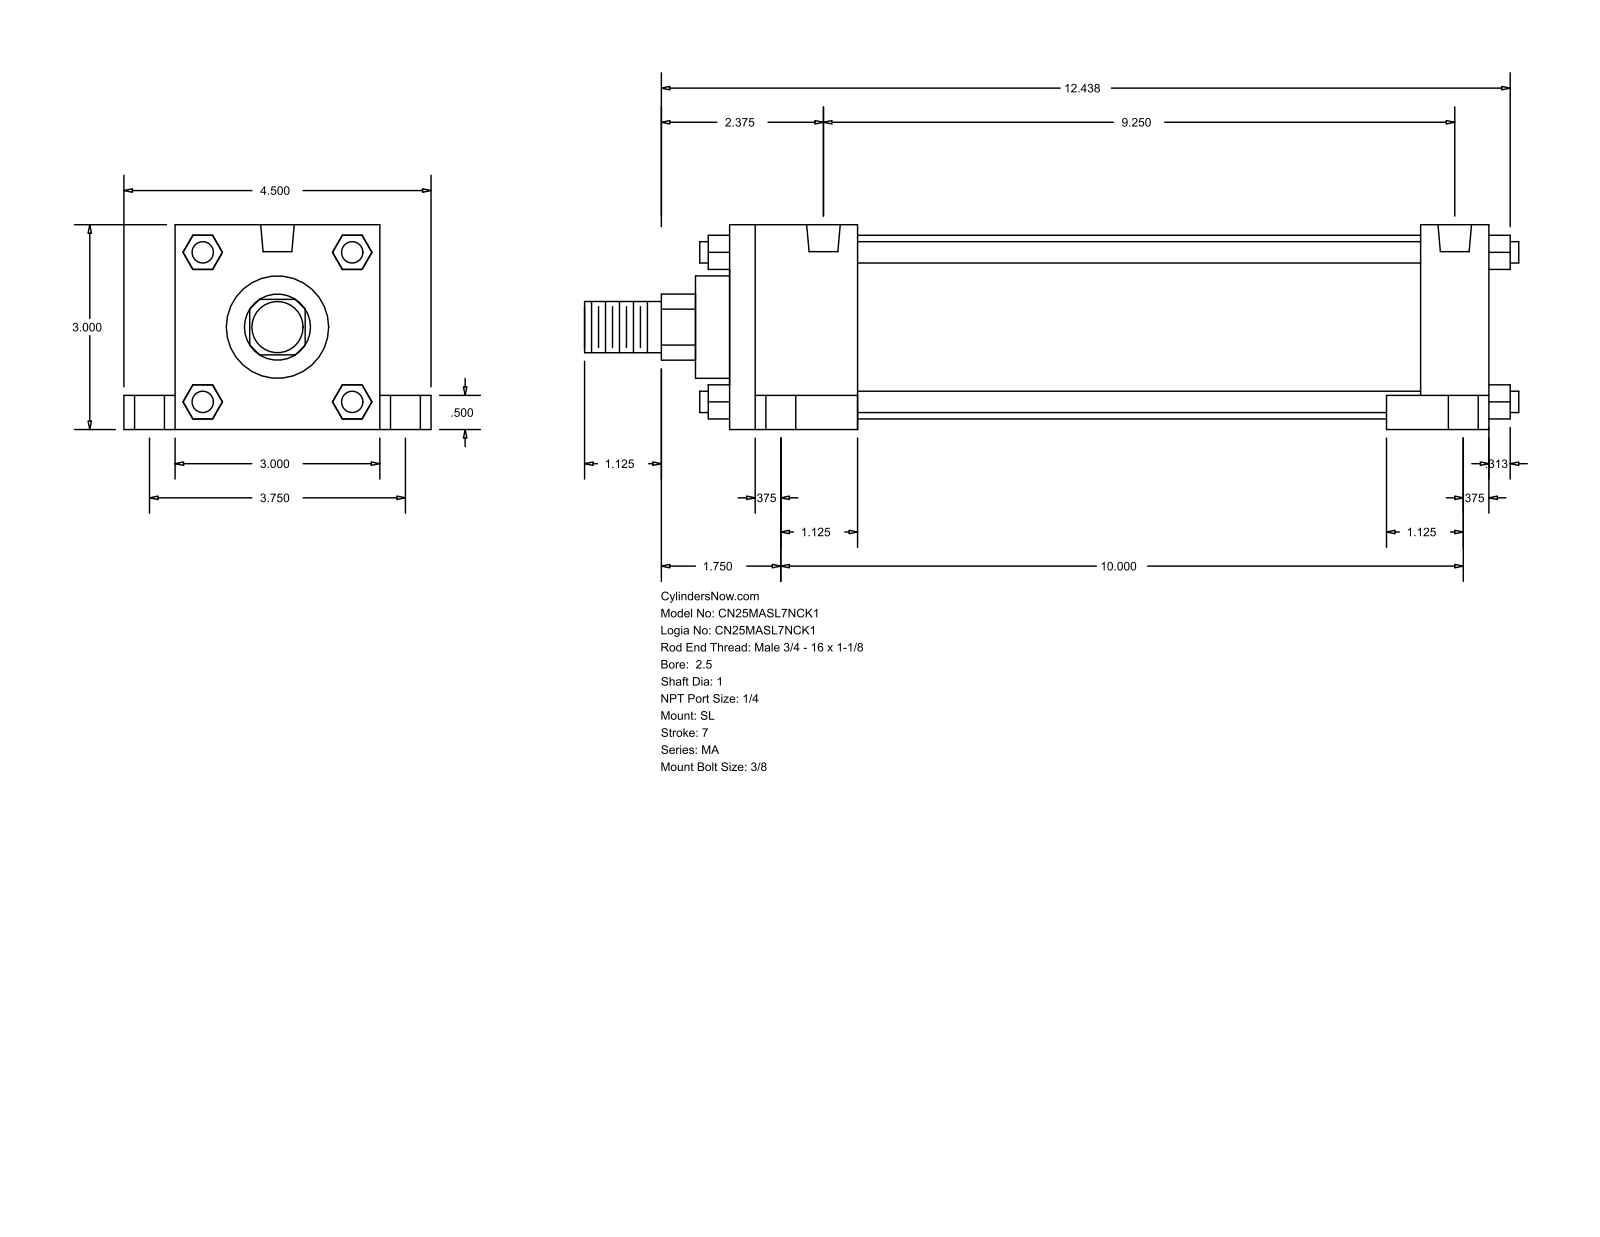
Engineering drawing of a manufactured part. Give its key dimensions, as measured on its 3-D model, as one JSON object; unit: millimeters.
{"part_name": "MA_SL__0250_1", "step_written_by": "GSSL Pune (CONFIG_CONTROL_DESIGN)", "units": "millimeters", "bodies": {"solids": 0, "faces": 148, "planar": 112, "cylindrical": 36, "other": 0}, "overall_size": [347.66, 114.3, 76.2], "round_holes": [[7.94, 4], [11.11, 4], [17.46, 4], [12.49, 2]], "round_bosses_or_shafts": [[7.94, 4], [68.33, 1], [38.1, 1], [25.4, 1], [19.05, 1]], "partial_cylinders_radius": [[12.29, 1]], "face_to_face_distances": [76.2, 282.58, 12.7, 47.63, 234.95, 257.17, 209.54, 25.41, 19.05, 95.25], "hole_center_spacings": [47.73, 50.2, 95.24, 234.94, 242.83, 254, 255.3, 271.27]}
